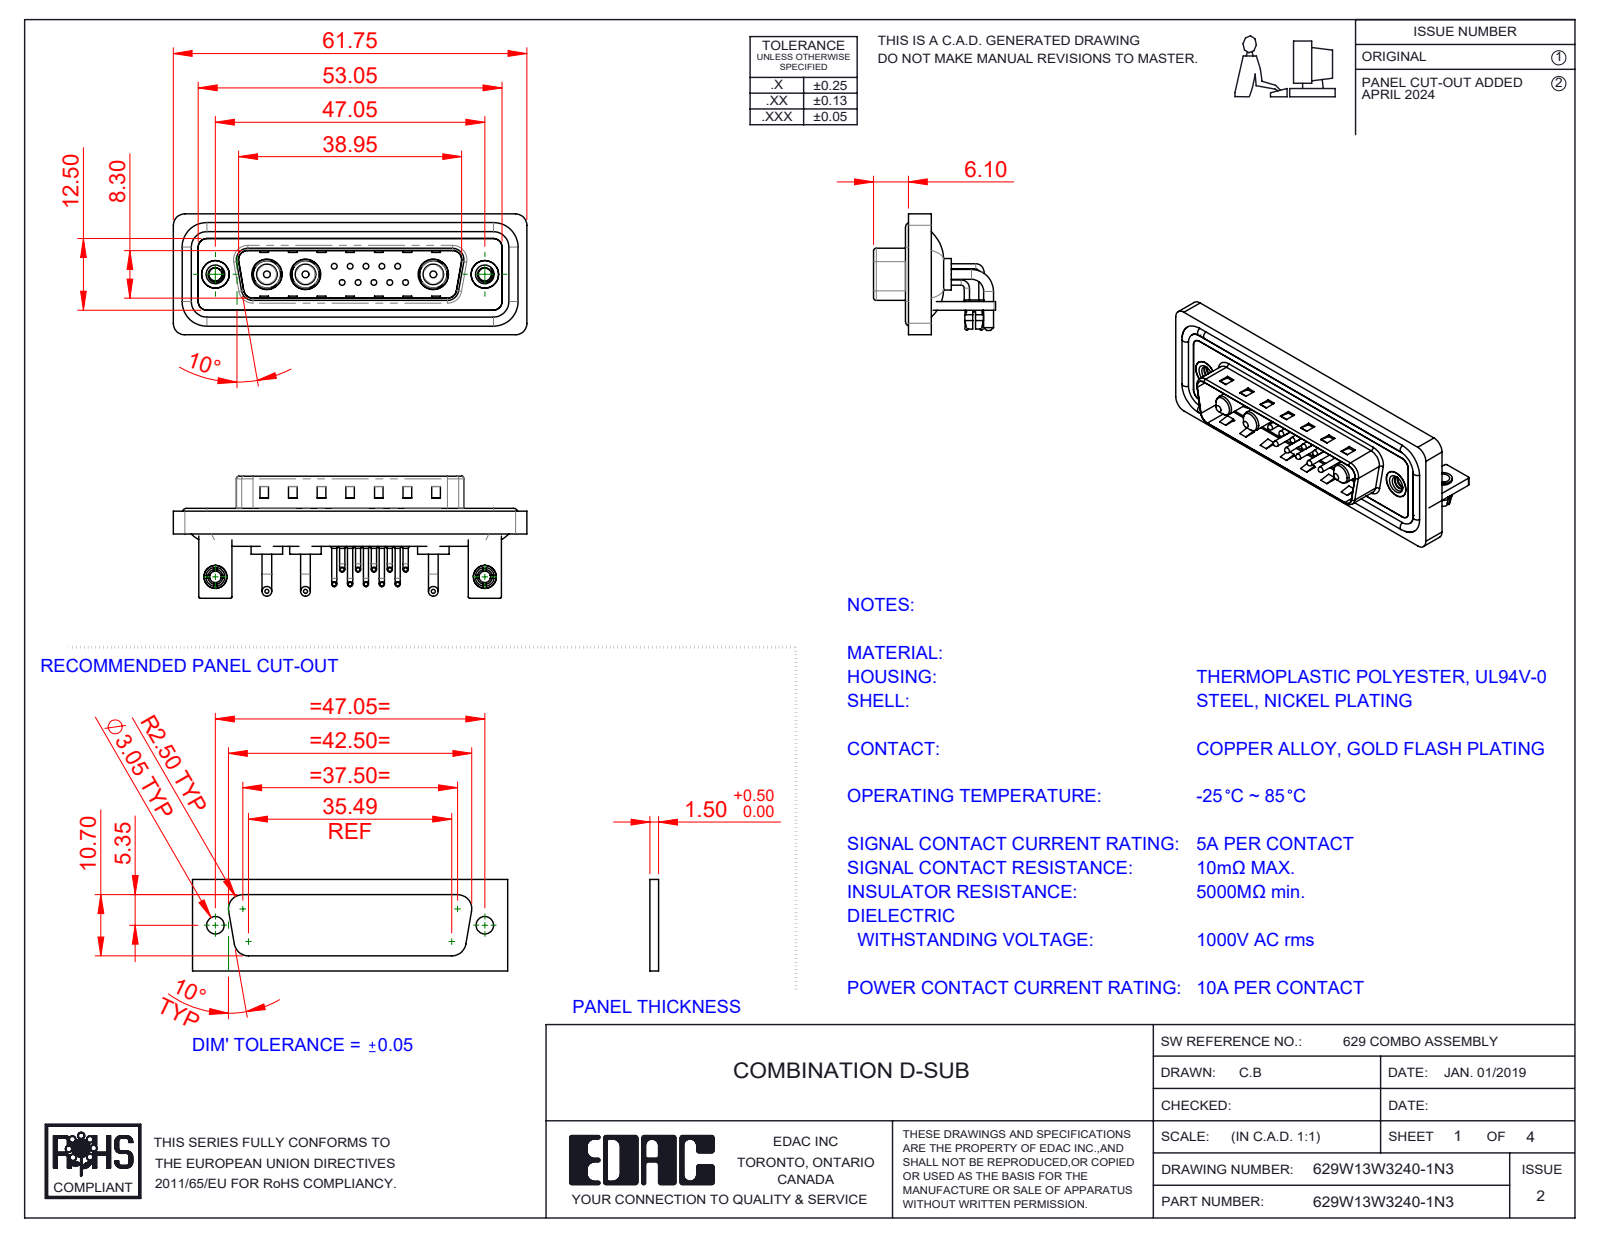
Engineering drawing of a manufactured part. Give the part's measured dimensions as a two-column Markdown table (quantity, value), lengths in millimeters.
| quantity | value |
| --- | --- |
| part name | 629Combo Board Lock; 629W13W3240-1N3; 629Combo Housing_13W3; 629Combo Waterproof Housing_25 Contacts (+7 more) |
| STEP written by | SolidWorks 2023 (CONFIG_CONTROL_DESIGN) |
| units | millimeters |
| bodies | 27 solids, 1844 faces (947 planar, 661 cylindrical, 236 other) |
| overall size | 61.75 × 21.3 × 21.1 |
| volume | 7 750 mm³ |
| surface area | 13 141 mm² |
| round holes (diameter × count) | 2 × 12, 0.75 × 10, 1.6 × 10, 4.85 × 3, 5.3 × 3, 2.26 × 2, 2.5 × 2, 3.2 × 2, 4 × 2, 4.8 × 2, 5 × 2 |
| round bosses / shafts (diameter × count) | 0.9 × 20, 1.5 × 10, 1 × 10, 0.65 × 10, 1.7 × 6, 1.6 × 4, 5.5 × 3, 5.2 × 3 |
| partial cylindrical surfaces (radius × count) | 2 × 19, 1.5 × 18, 0.25 × 16, 1.01 × 10, 0.5 × 9, 1.6 × 8, 0.6 × 4, 0.65 × 4 |
| main face-to-face distances | 0.4, 1.5, 0.8, 2.9, 2.1, 1.1, 4.1, 1.6, 3.7, 4.5 |
| hole center spacings | 3.16, 2.77, 5.04, 5.54, 7.49, 5.03, 8.31, 10.11 |
